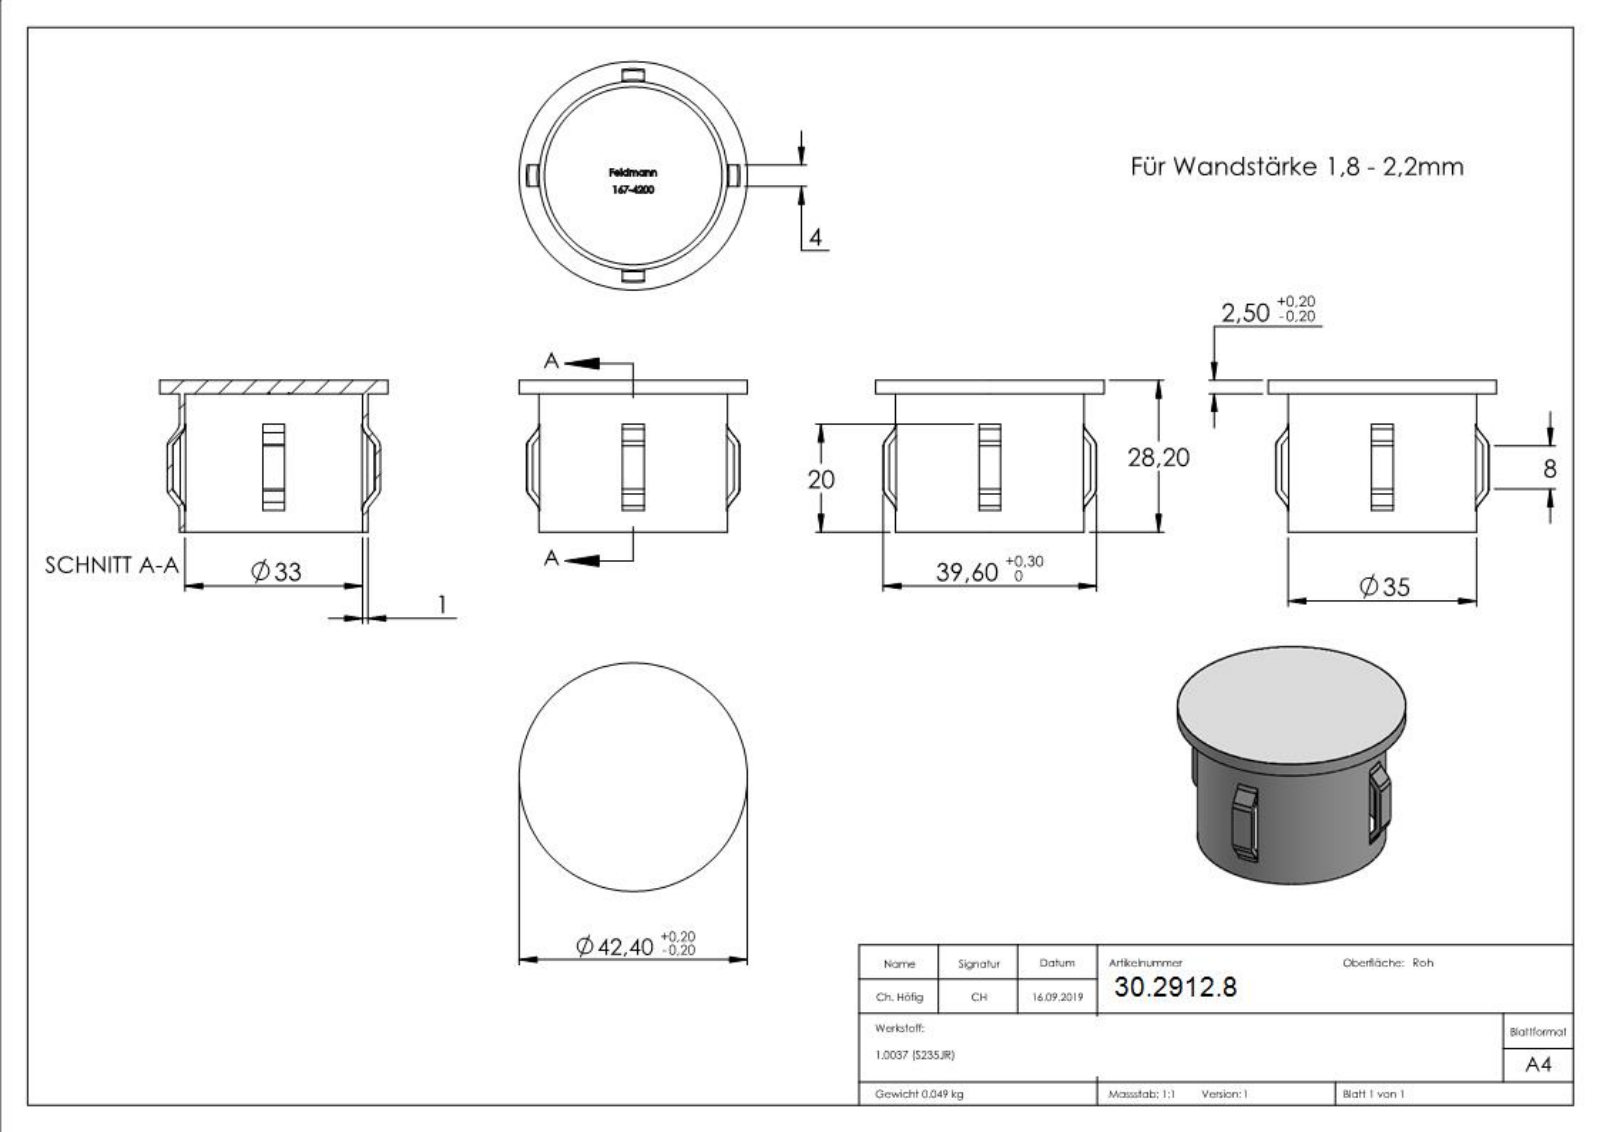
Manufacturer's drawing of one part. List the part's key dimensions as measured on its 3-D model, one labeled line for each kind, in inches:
Part name (STEP PRODUCT): 167-4200
STEP written by: SolidWorks 2015 (CONFIG_CONTROL_DESIGN)
Units: inches
Bodies: 1 solid, 292 faces (135 planar, 16 cylindrical, 141 other)
Overall size (bounding box): 1.669 × 1.669 × 1.11
Volume: 0.384 in³ · Surface area: 13.83 in²
Round holes (diameter × count): ⌀1.299 ×1
Round bosses / shafts (diameter × count): ⌀1.669 ×1, ⌀1.378 ×1
Partial cylindrical surfaces — rounded edges, fillets, slot ends (radius × count): R0.74 ×1, R0.78 ×1
Main face-to-face distances: 0.098, 0.157, 1.012, 1.11, 0.094, 1.016, 0.153, 0.079, 0.117, 0.112
